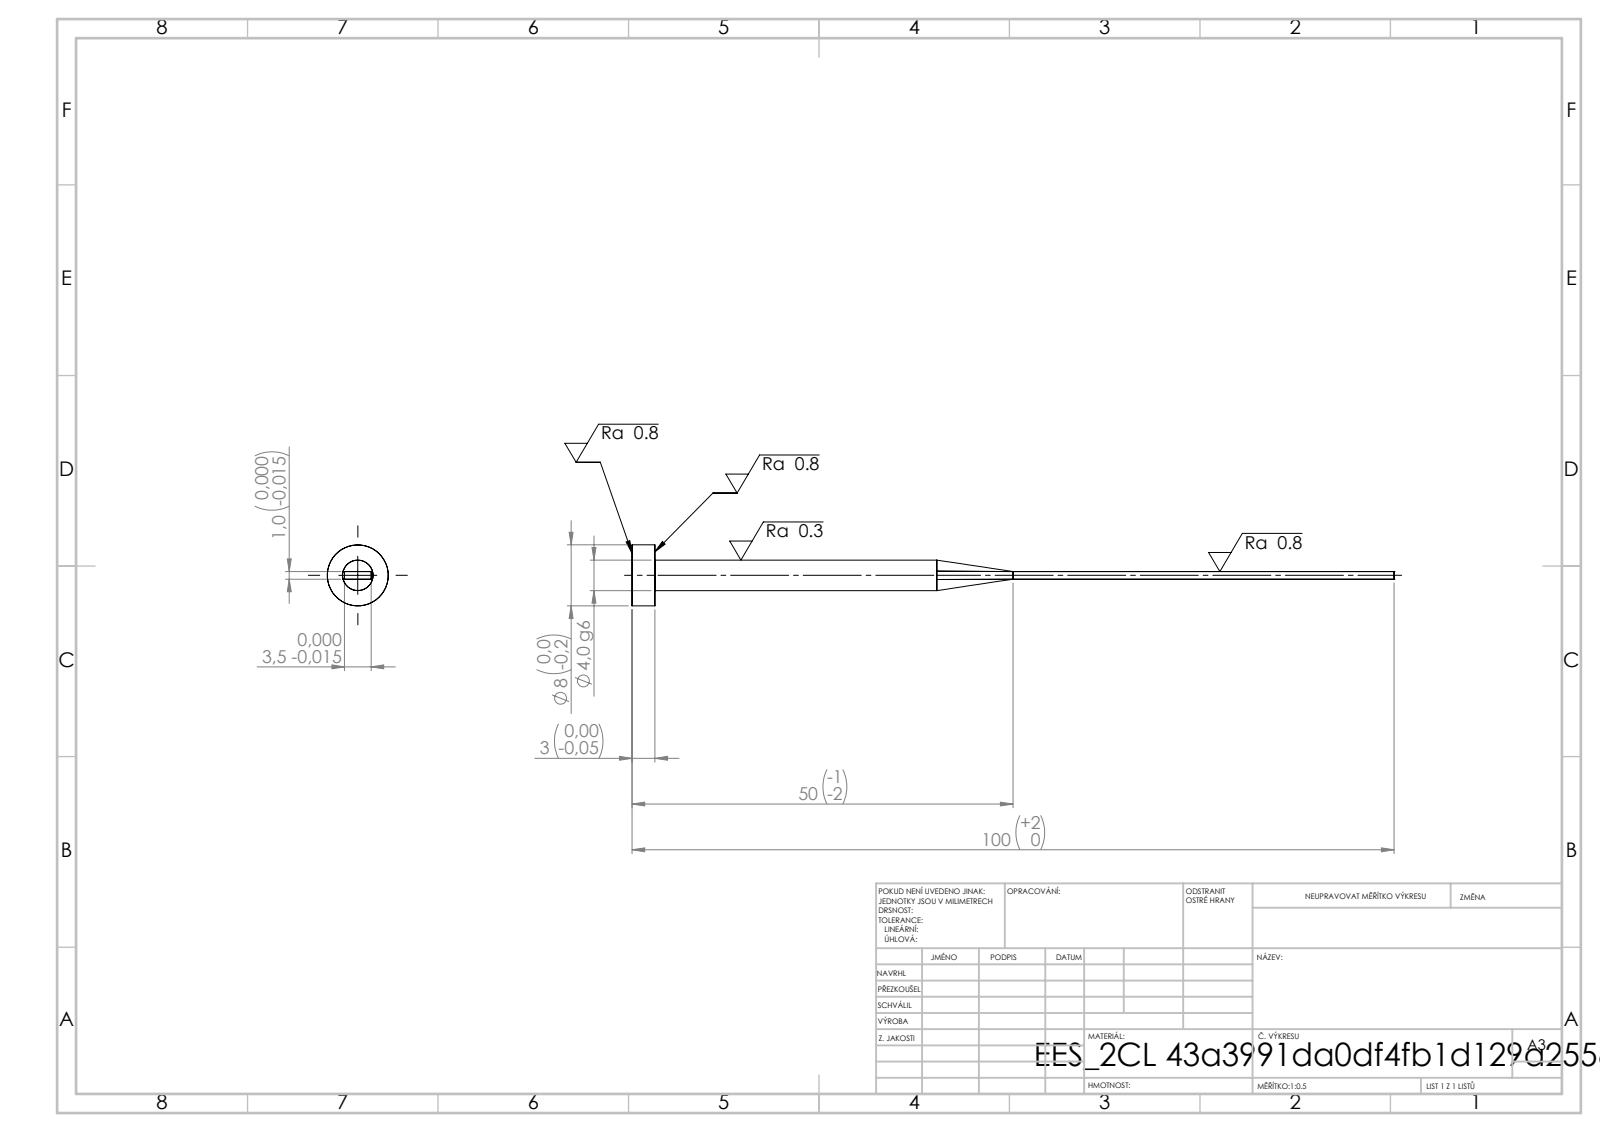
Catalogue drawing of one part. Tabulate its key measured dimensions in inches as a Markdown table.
| quantity | value |
| --- | --- |
| STEP written by | SolidWorks 2019 (CONFIG_CONTROL_DESIGN) |
| units | inches |
| bodies | 1 solid, 15 faces (7 planar, 4 cylindrical, 4 other) |
| overall size | 3.937 × 0.315 × 0.315 |
| volume | 0.053 in³ |
| surface area | 1.838 in² |
| round bosses / shafts (diameter × count) | 0.315 × 1, 0.157 × 1 |
| main face-to-face distances | 0.039, 0.138, 0.118, 3.937, 3.819 |
